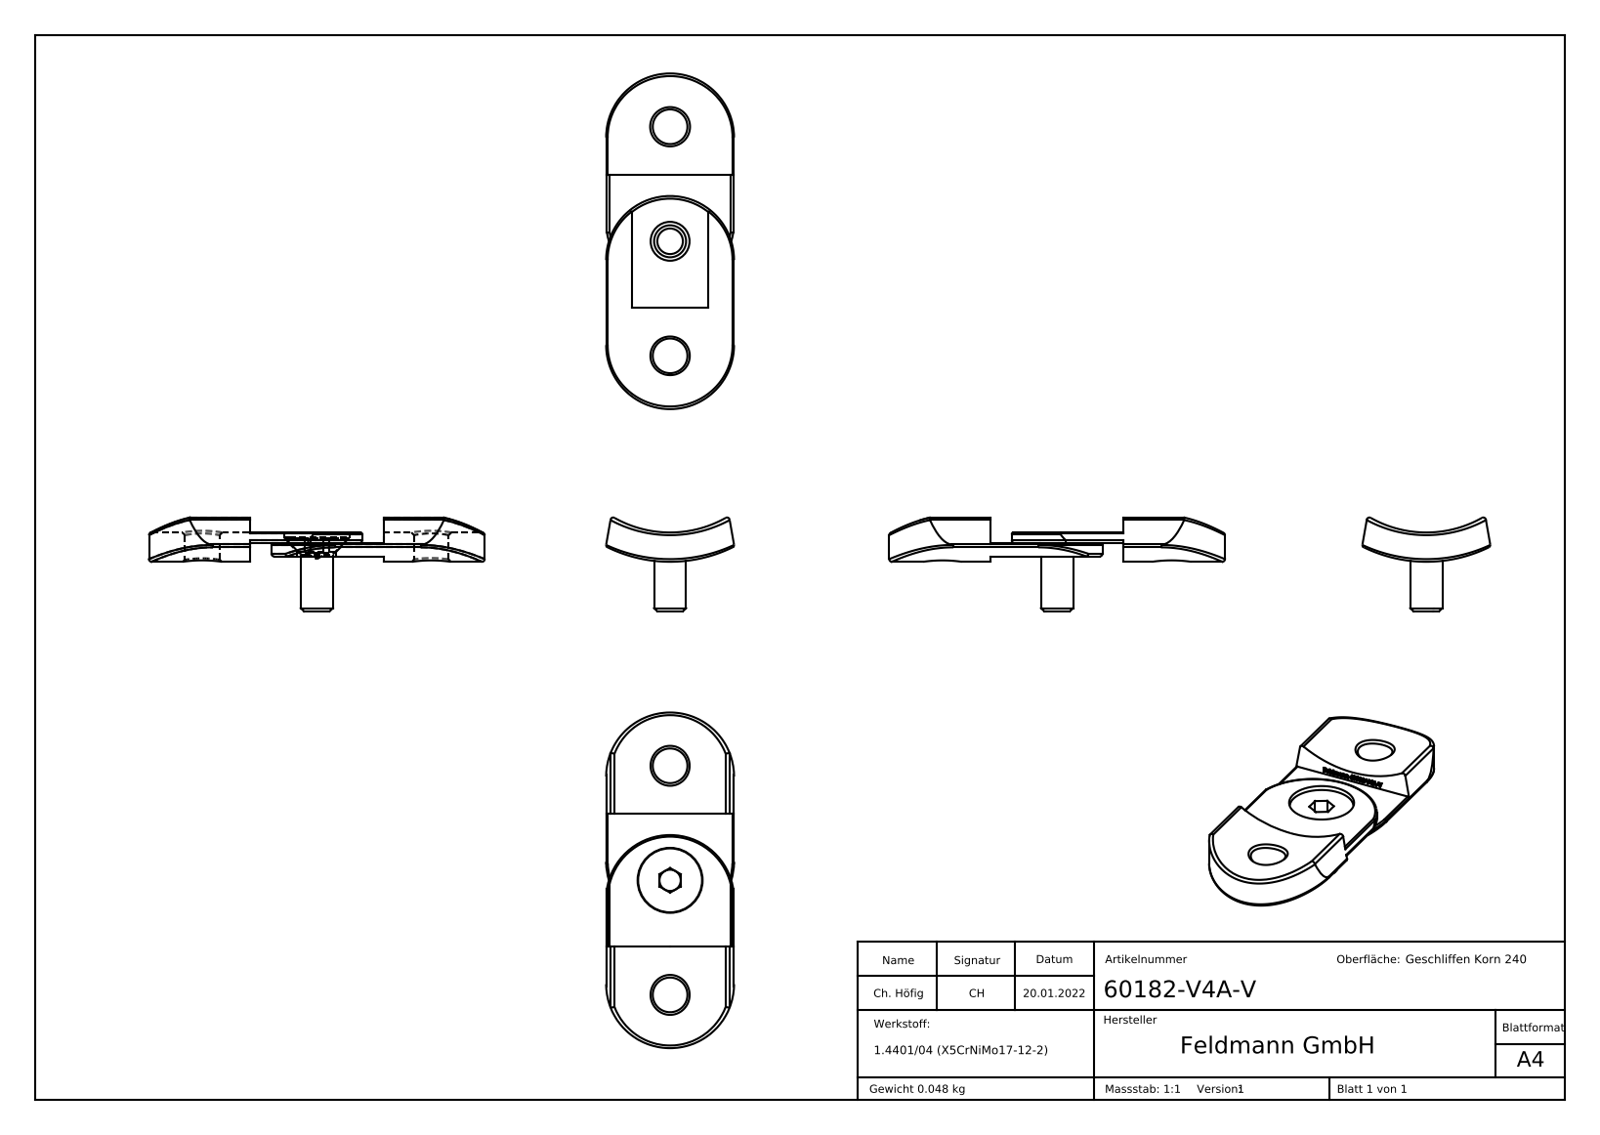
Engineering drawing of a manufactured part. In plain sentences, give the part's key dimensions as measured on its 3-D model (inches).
The part is named "60182-V4A-V; 6018X-240-V Teil2_60182-V4A-V Teil2; DIN7991 M6x14_DIN7991 M6x14; DIN7991 M6x14 (+3 more)". Its 3-D file was written by "SolidWorks 2018 (CONFIG_CONTROL_DESIGN)". It is 3 solids with 326 faces: 170 planar, 38 cylindrical and 118 other. Overall it measures 2.48 by 0.945 by 0.693 inches. Its volume is 0.367 cubic inches and its surface area 7.242 square inches. Round holes: 2 of diameter 0.256, 1 of diameter 0.287, 1 of diameter 0.48. Round bosses or shafts: 1 of diameter 0.472, 1 of diameter 0.236. Partial cylindrical surfaces (rounded edges, fillets, slot ends): 6 of radius 0.02, 4 of radius 0.012, 4 of radius 0.472, 1 of radius 0.835, 1 of radius 1.051. The main face-to-face distances are 0.079, 0.098, 0.177, 0.146, 0.047, 0.031, 0.984, 0.406, 0.504, 0.551. The hole center spacings are 0.846, 1.693.
